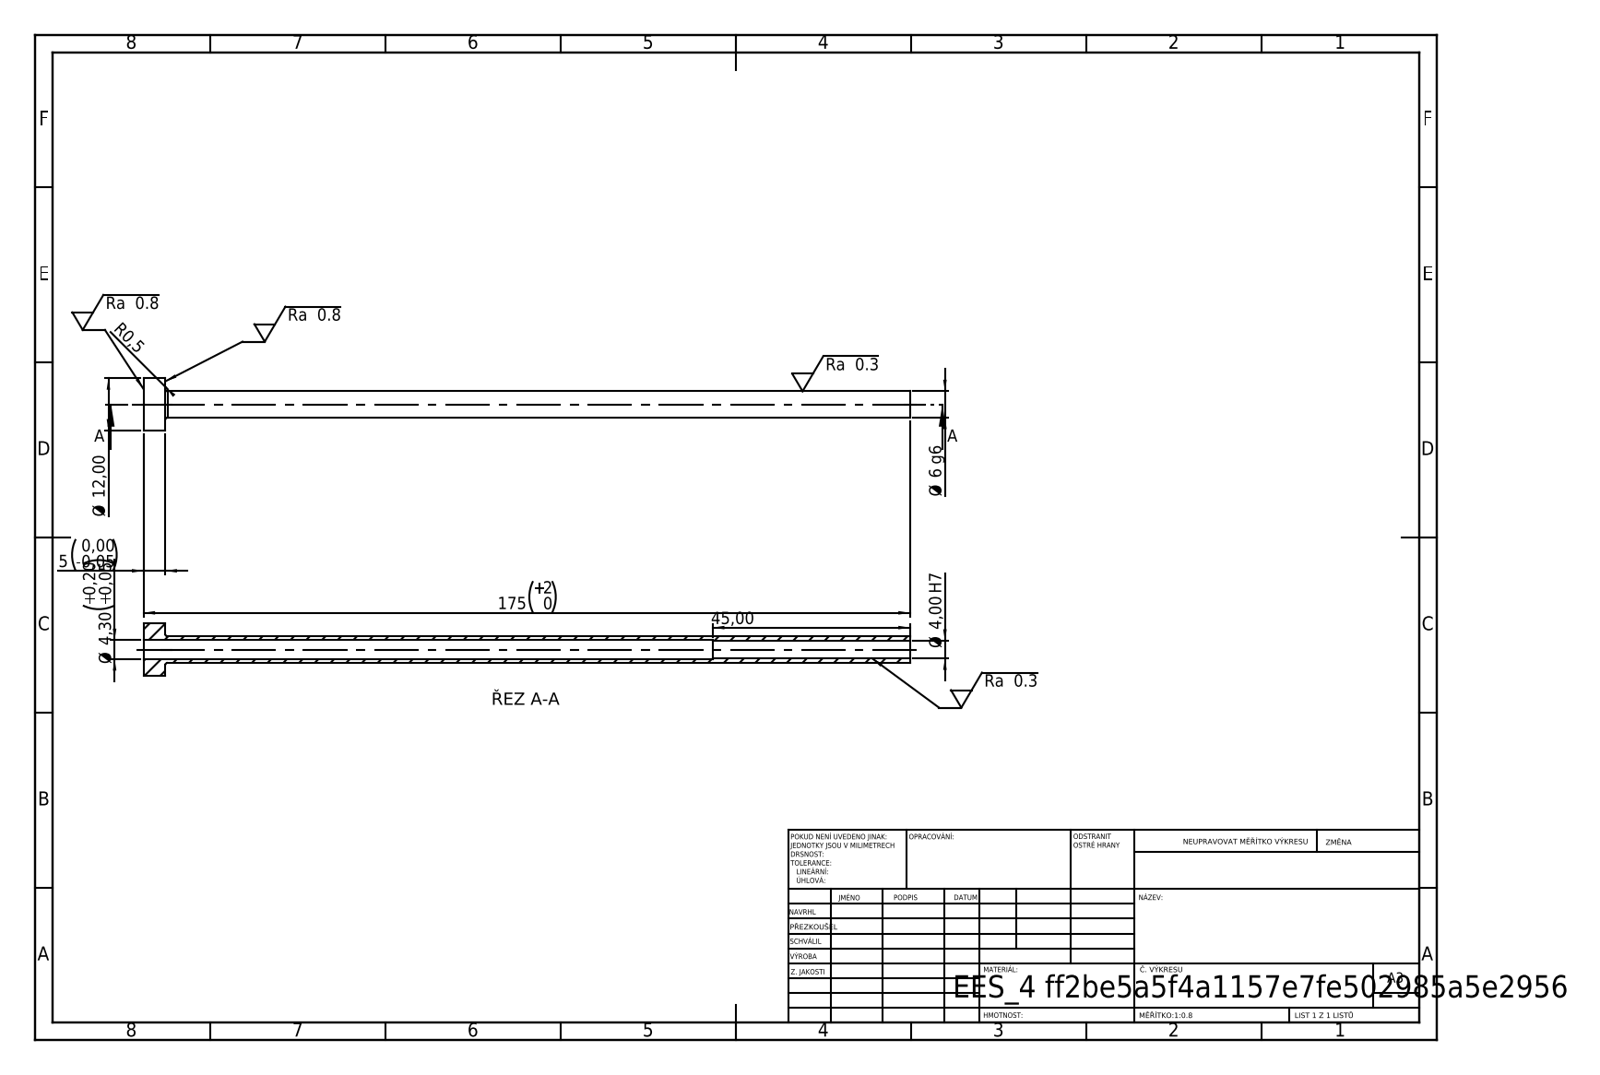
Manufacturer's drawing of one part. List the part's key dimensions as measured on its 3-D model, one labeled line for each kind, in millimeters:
STEP written by: SolidWorks 2019 (CONFIG_CONTROL_DESIGN)
Units: millimetres
Bodies: 1 solid, 14 faces (4 planar, 8 cylindrical, 2 other)
Overall size (bounding box): 175 × 12 × 12
Volume: 2 920 mm³ · Surface area: 5 912 mm²
Round holes (diameter × count): ⌀4 ×1, ⌀4.3 ×1
Round bosses / shafts (diameter × count): ⌀12 ×1, ⌀6 ×1
Main face-to-face distances: 5, 175, 170, 130, 125, 45
